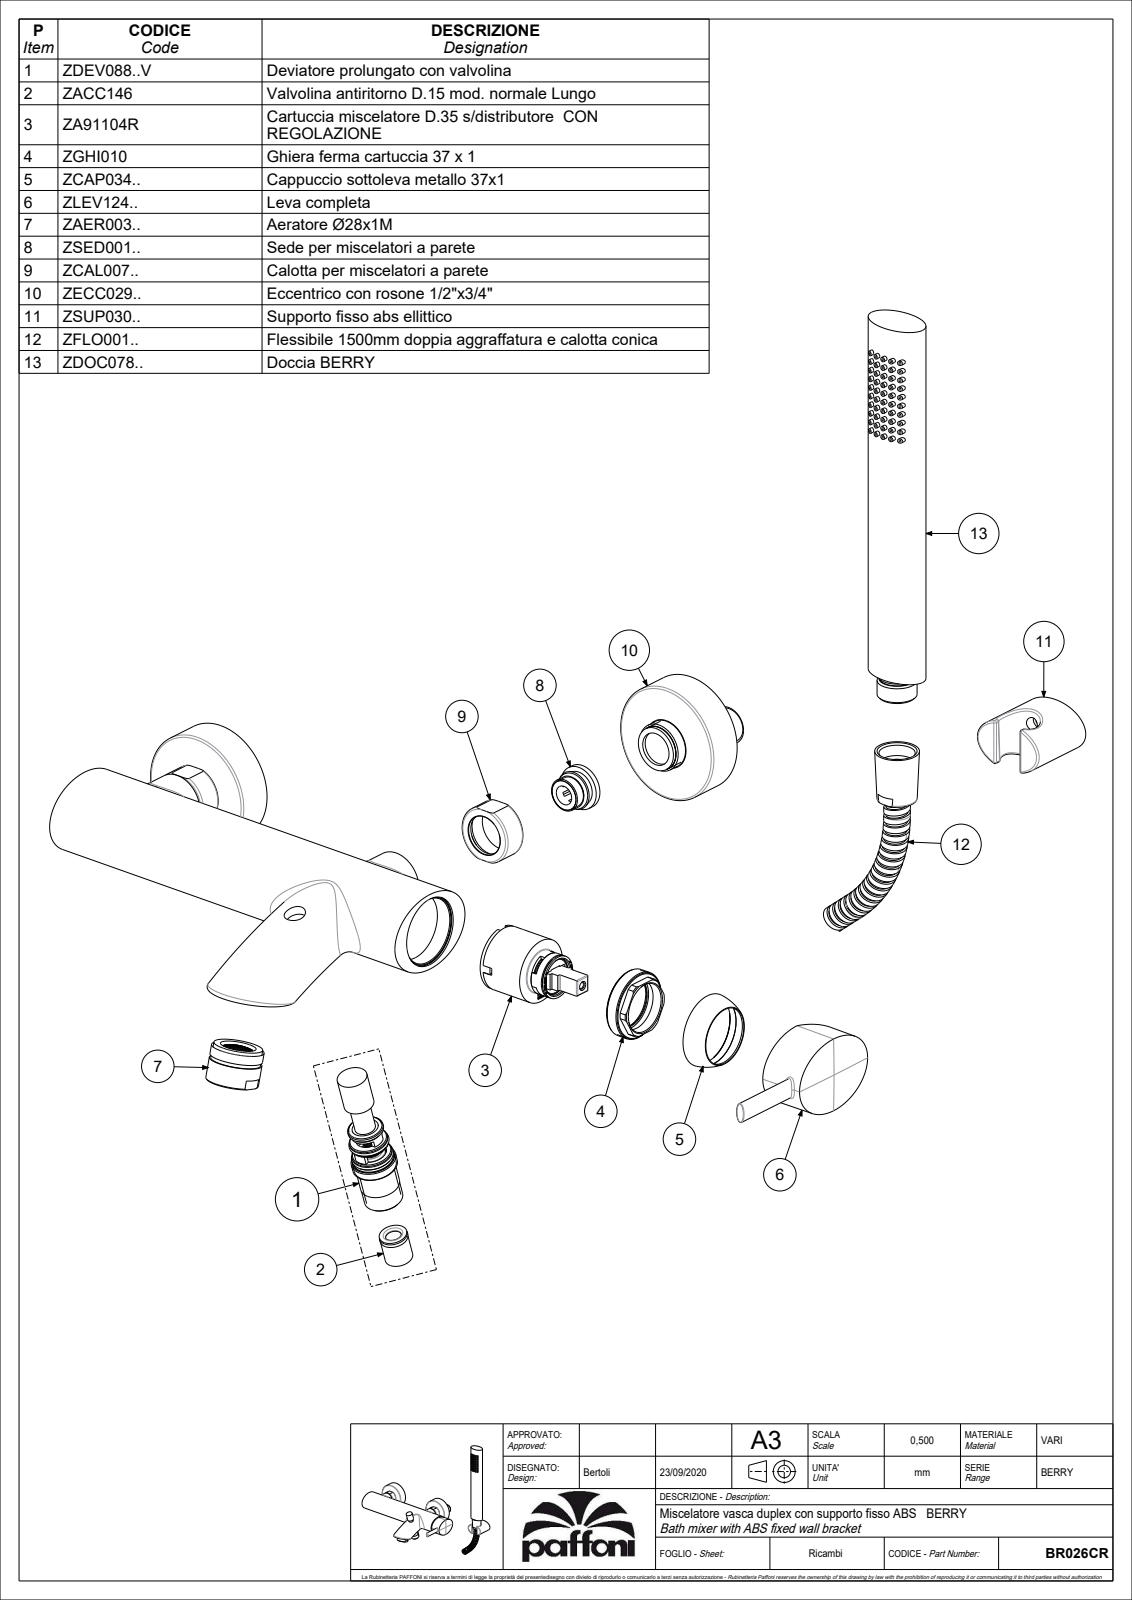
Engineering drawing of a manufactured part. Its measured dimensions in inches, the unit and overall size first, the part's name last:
Units: inches
Overall size (bounding box): 13.888 × 12.61 × 6.996
Round holes (diameter × count): ⌀0.039 ×50, ⌀0.157 ×4, ⌀0.965 ×3, ⌀0.984 ×3, ⌀0.138 ×2, ⌀0.197 ×2, ⌀0.276 ×2, ⌀0.295 ×2, ⌀0.413 ×2, ⌀0.657 ×2, ⌀0.709 ×2, ⌀0.85 ×2
Round bosses / shafts (diameter × count): ⌀0.098 ×50, ⌀0.945 ×3, ⌀2.5 ×2, ⌀1.228 ×2, ⌀1.102 ×2, ⌀1.063 ×2, ⌀1.043 ×2, ⌀1.398 ×1
Partial cylindrical surfaces — rounded edges, fillets, slot ends (radius × count): R0.02 ×27, R0.006 ×11, R0.039 ×8, R0.012 ×4, R0.049 ×4, R0.157 ×1, R0.217 ×1, R0.256 ×1
Main face-to-face distances: 0.138, 1.555, 0.024, 1.531, 1.417, 1.394, 0.394, 0.315, 0.118, 0.472
Hole centre spacings: 0.197, 0.44, 0.278, 0.394, 0.622, 0.812, 0.591, 1.004
Volume: 28.45 in³ · Surface area: 362.2 in²
Bodies: 4 solids, 3301 faces (2228 planar, 599 cylindrical, 474 other)
Part name (STEP PRODUCT): BR026CR
STEP written by: CREO PARAMETRIC BY PTC INC, 2020044 (CONFIG_CONTROL_DESIGN)
